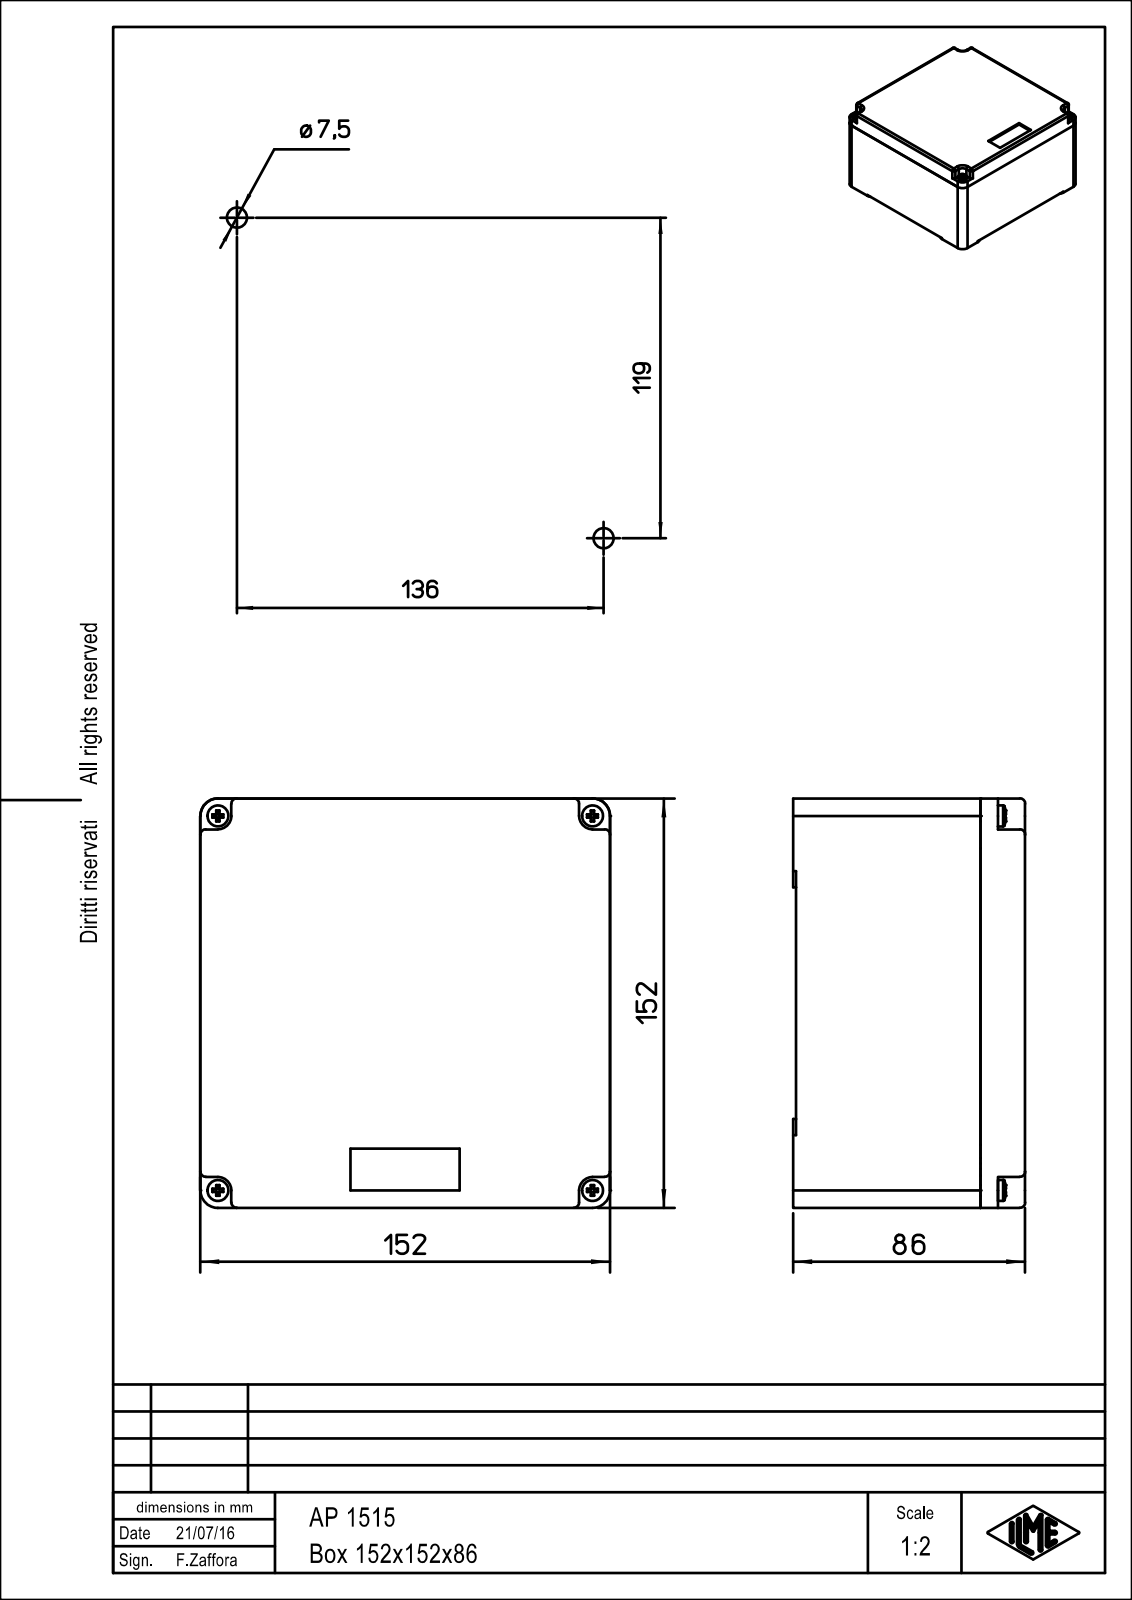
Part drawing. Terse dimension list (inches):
name: BOX; COVER; AP_1515
written by: PTC Creo Elements/Direct Modeling 19.0B 21-Mar-2015 (C) Parametric Technology GmbH (AUTOMOTIVE_DESIGN)
unit: in
bodies: 2 solids, 995 faces (786 planar, 169 cylindrical, 40 other)
size: 5.985 × 5.985 × 3.386
volume: 23.91 in³; area: 318.7 in²
holes: 6× ⌀0.13, 4× ⌀0.177, 2× ⌀0.228, 2× ⌀0.295, 1× ⌀0.417, 1× ⌀0.418
bosses: 4× ⌀0.307, 4× ⌀0.157, 2× ⌀0.244, 2× ⌀0.236, 1× ⌀0.276
rounds: 22× R0.013, 17× R0.079, 12× R0.236, 8× R0.256, 6× R0.197, 6× R0.315, 4× R0.011, 4× R0.011
face distances: 0.118, 3.228, 5.984, 3.346, 3.11, 0.172, 5.812, 5.812, 0.172, 5.64
hole spacings: 5.472, 7.739, 5.02, 5.428, 0.398, 0.459, 0.463, 0.729
